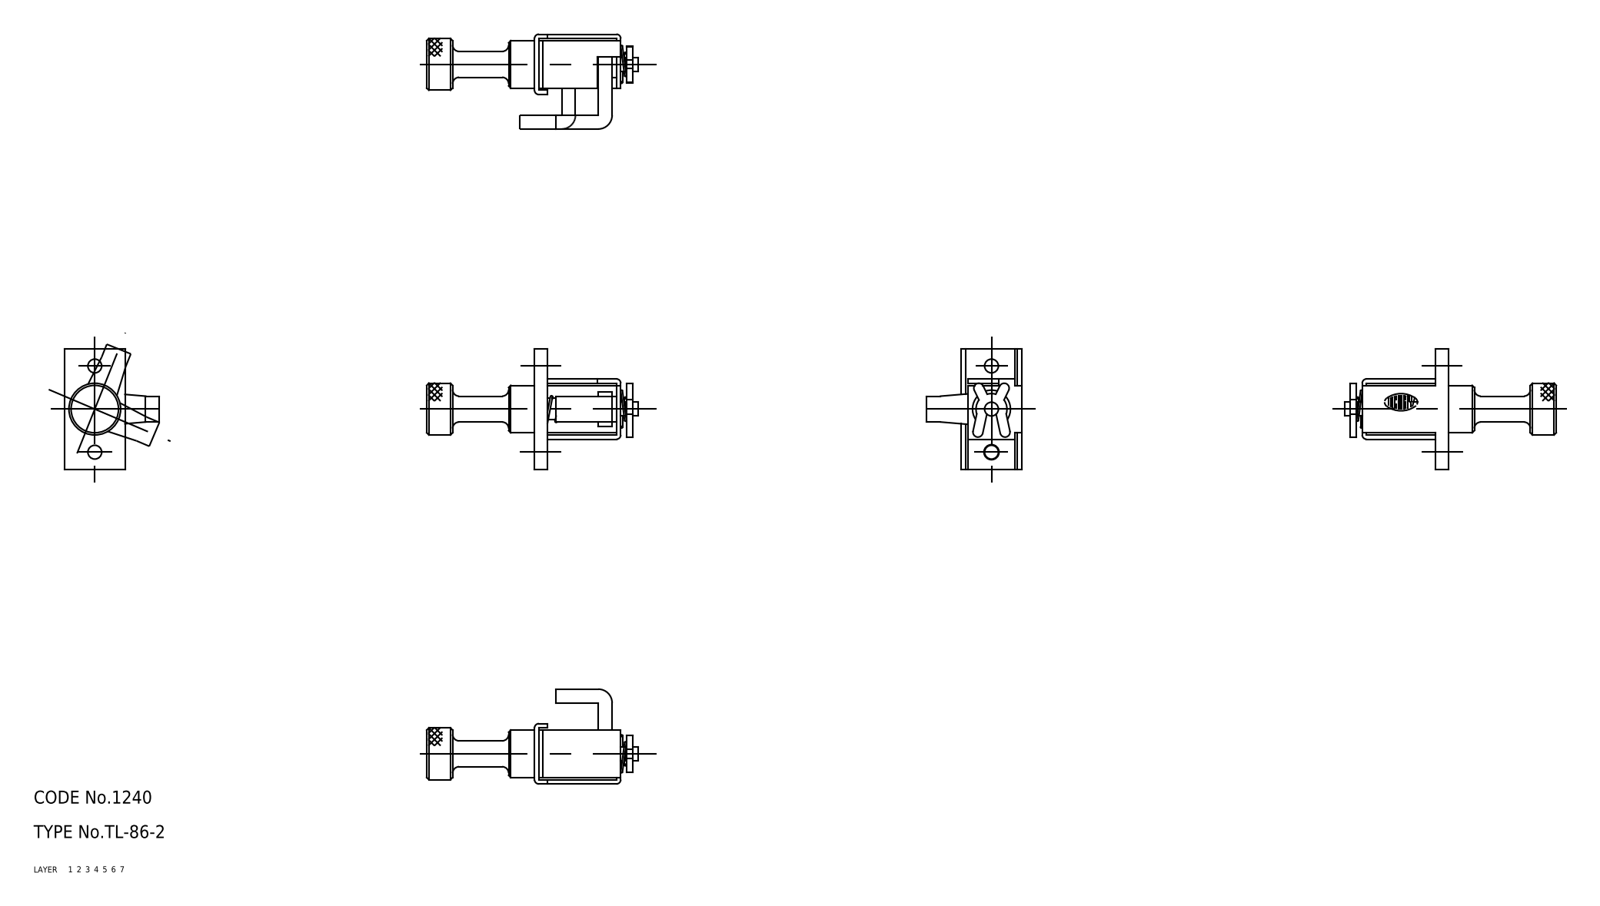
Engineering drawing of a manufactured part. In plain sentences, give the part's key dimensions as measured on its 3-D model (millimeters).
The part is named "collar; spring_2; spring_1; retainer (+4 more)". Its 3-D file was written by "CADfix (AUTOMOTIVE_DESIGN)". It is 7 solids with 268 faces: 0 planar, 0 cylindrical and 268 other. Overall it measures 49 by 28 by 22 millimeters. Its volume is 3 961 cubic millimeters and its surface area 5 332 square millimeters.
